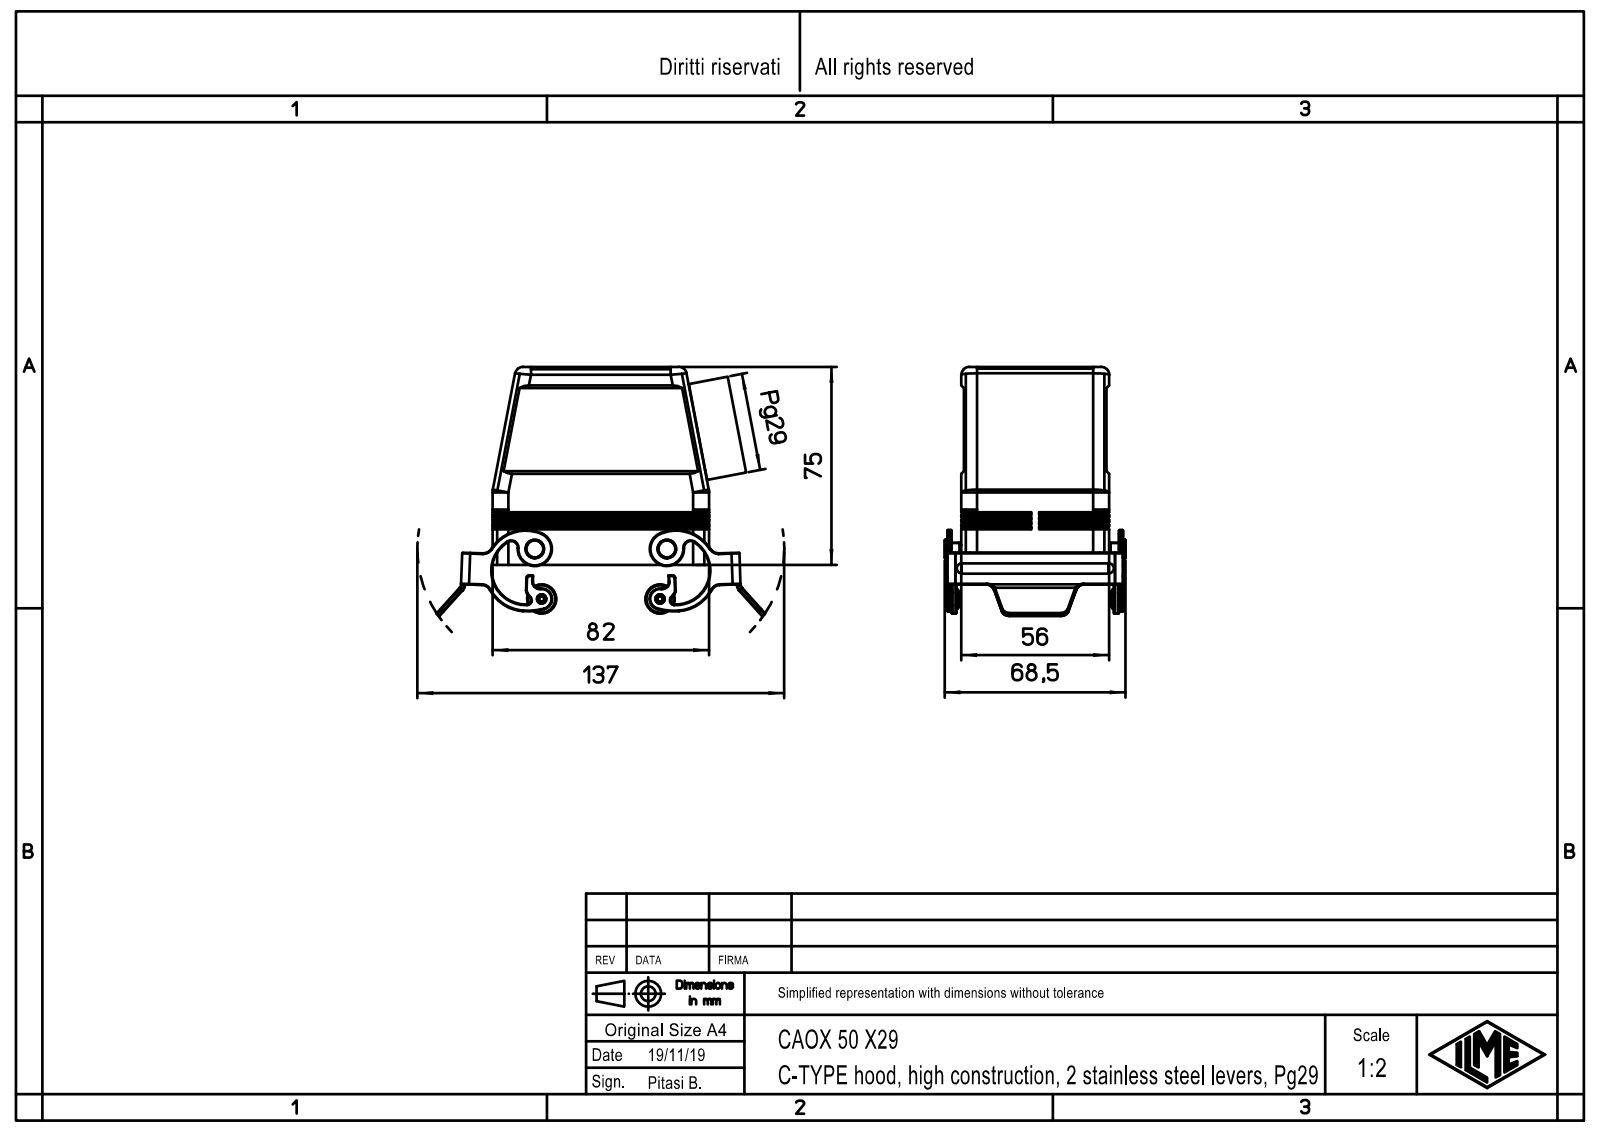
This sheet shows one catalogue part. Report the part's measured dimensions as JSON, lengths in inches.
{"part_name": "CAOX 50 X29; CAOX 50 X29.stp", "step_written_by": "Creo Elements/Direct Modeling 20.1B 02-Apr-2019 (C) Parametric Technology GmbH (AUTOMOTIVE_DESIGN)", "units": "inches", "bodies": {"solids": 1, "faces": 717, "planar": 297, "cylindrical": 326, "other": 94}, "overall_size": [4.834, 3.766, 2.697], "volume_in3": 5.093, "surface_area_in2": 92.6, "round_holes": [[0.097, 8], [0.138, 8], [0.197, 4], [0.079, 2], [0.122, 2], [1.318, 1], [1.397, 1]], "round_bosses_or_shafts": [[0.276, 4], [0.189, 4], [0.433, 2], [0.138, 2], [0.118, 2], [1.535, 1]], "partial_cylinders_radius": [[0.118, 20], [0.01, 14], [0.079, 12], [0.236, 10], [0.059, 6], [0.138, 6], [0.217, 6], [0.098, 4]], "face_to_face_distances": [0.118, 2.087, 0.039, 1.969, 0.079, 2.165, 2.047, 0.325, 0.059, 2.205], "hole_center_spacings": [0.63, 0.945, 2.598, 2.674, 2.765, 0.315, 0.751, 1.575]}
